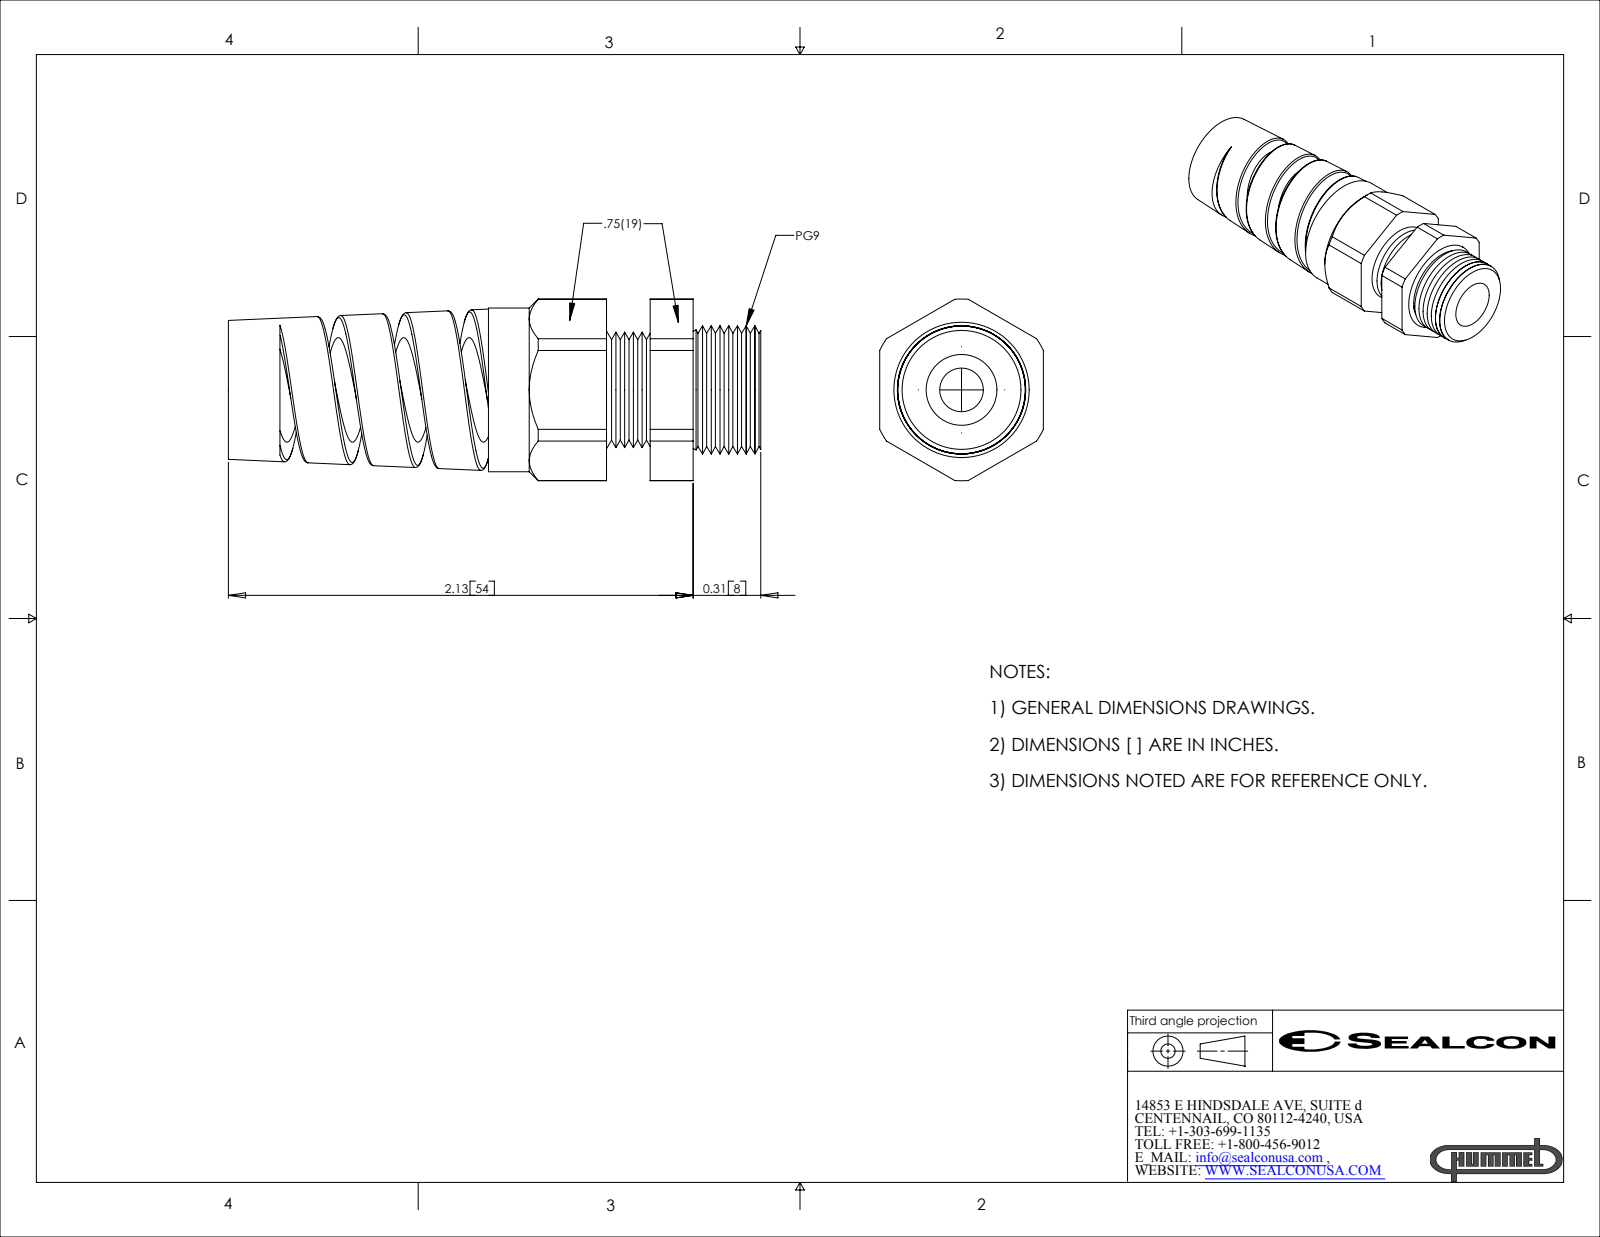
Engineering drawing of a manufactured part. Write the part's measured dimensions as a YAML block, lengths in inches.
part_name: "CF09BR-BK"
step_written_by: "SolidWorks 2007 (CONFIG_CONTROL_DESIGN)"
units: inches
bodies: {solids: 2, faces: 140, planar: 24, cylindrical: 31, other: 85}
overall_size: [2.44, 0.833, 0.75]
volume: 0.559
surface_area: 12.04
round_holes:
  - {diameter: 0.2, count: 1}
  - {diameter: 0.48, count: 1}
  - {diameter: 0.54, count: 1}
round_bosses_or_shafts:
  - {diameter: 0.75, count: 1}
partial_cylinders:
  - {radius: 0.25, count: 1}
  - {radius: 0.416, count: 1}
face_to_face_distances: [0.75, 0.2, 0.75, 0.397, 0.197, 0.707, 0.507, 0.31, 1.733, 1.933]
